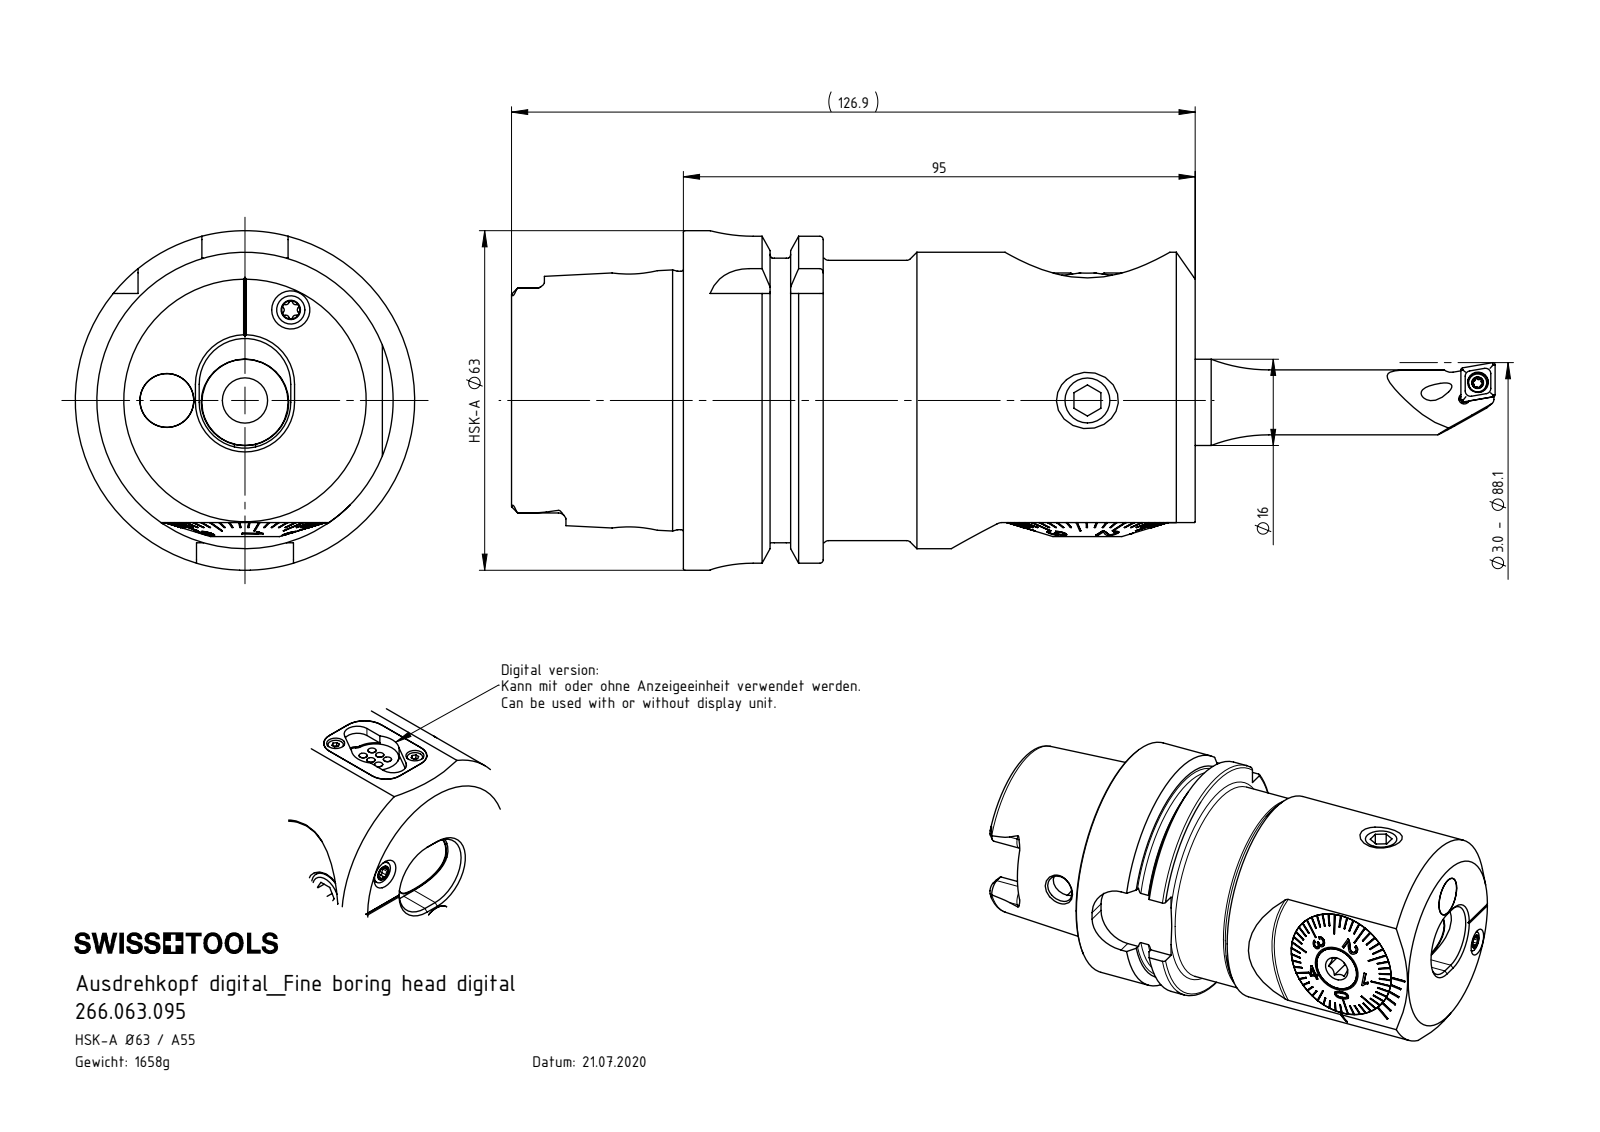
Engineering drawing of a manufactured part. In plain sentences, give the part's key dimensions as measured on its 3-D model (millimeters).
The part is named "Fxx-BG7.DA1.0xx_A_F55; DIN 3771 - 25x1.5; PEF-DA1.010.032_A; A55-BG2.013.005_C (+8 more)". Its 3-D file was written by "SolidWorks 2017 (AUTOMOTIVE_DESIGN)". It is 27 solids with 1268 faces: 514 planar, 329 cylindrical and 425 other. Overall it measures 180.15 by 63 by 63 millimeters. Its volume is 235 668 cubic millimeters and its surface area 68 956 square millimeters. Round holes: 4 of diameter 3.2, 3 of diameter 1.6, 3 of diameter 3.3, 3 of diameter 4.2, 3 of diameter 8.5, 2 of diameter 2.2, 2 of diameter 3, 2 of diameter 10, 1 of diameter 4.4, 1 of diameter 6.1, 1 of diameter 7.5, 1 of diameter 8. Round bosses or shafts: 6 of diameter 1.9, 3 of diameter 10, 2 of diameter 18, 2 of diameter 5.25, 2 of diameter 4, 2 of diameter 3.8, 2 of diameter 2, 1 of diameter 63. Partial cylindrical surfaces (rounded edges, fillets, slot ends): 12 of radius 0.34, 12 of radius 0.59, 8 of radius 1.2, 6 of radius 1.1, 6 of radius 1.4, 4 of radius 2.88, 4 of radius 4.5, 4 of radius 8. The main face-to-face distances are 95, 16, 3.7, 2, 4, 25.95, 69.05, 9.95, 85.05, 5.3. The hole center spacings are 4.1, 4.32, 7.25, 8.45, 9.52, 12, 12.68, 14.5.
